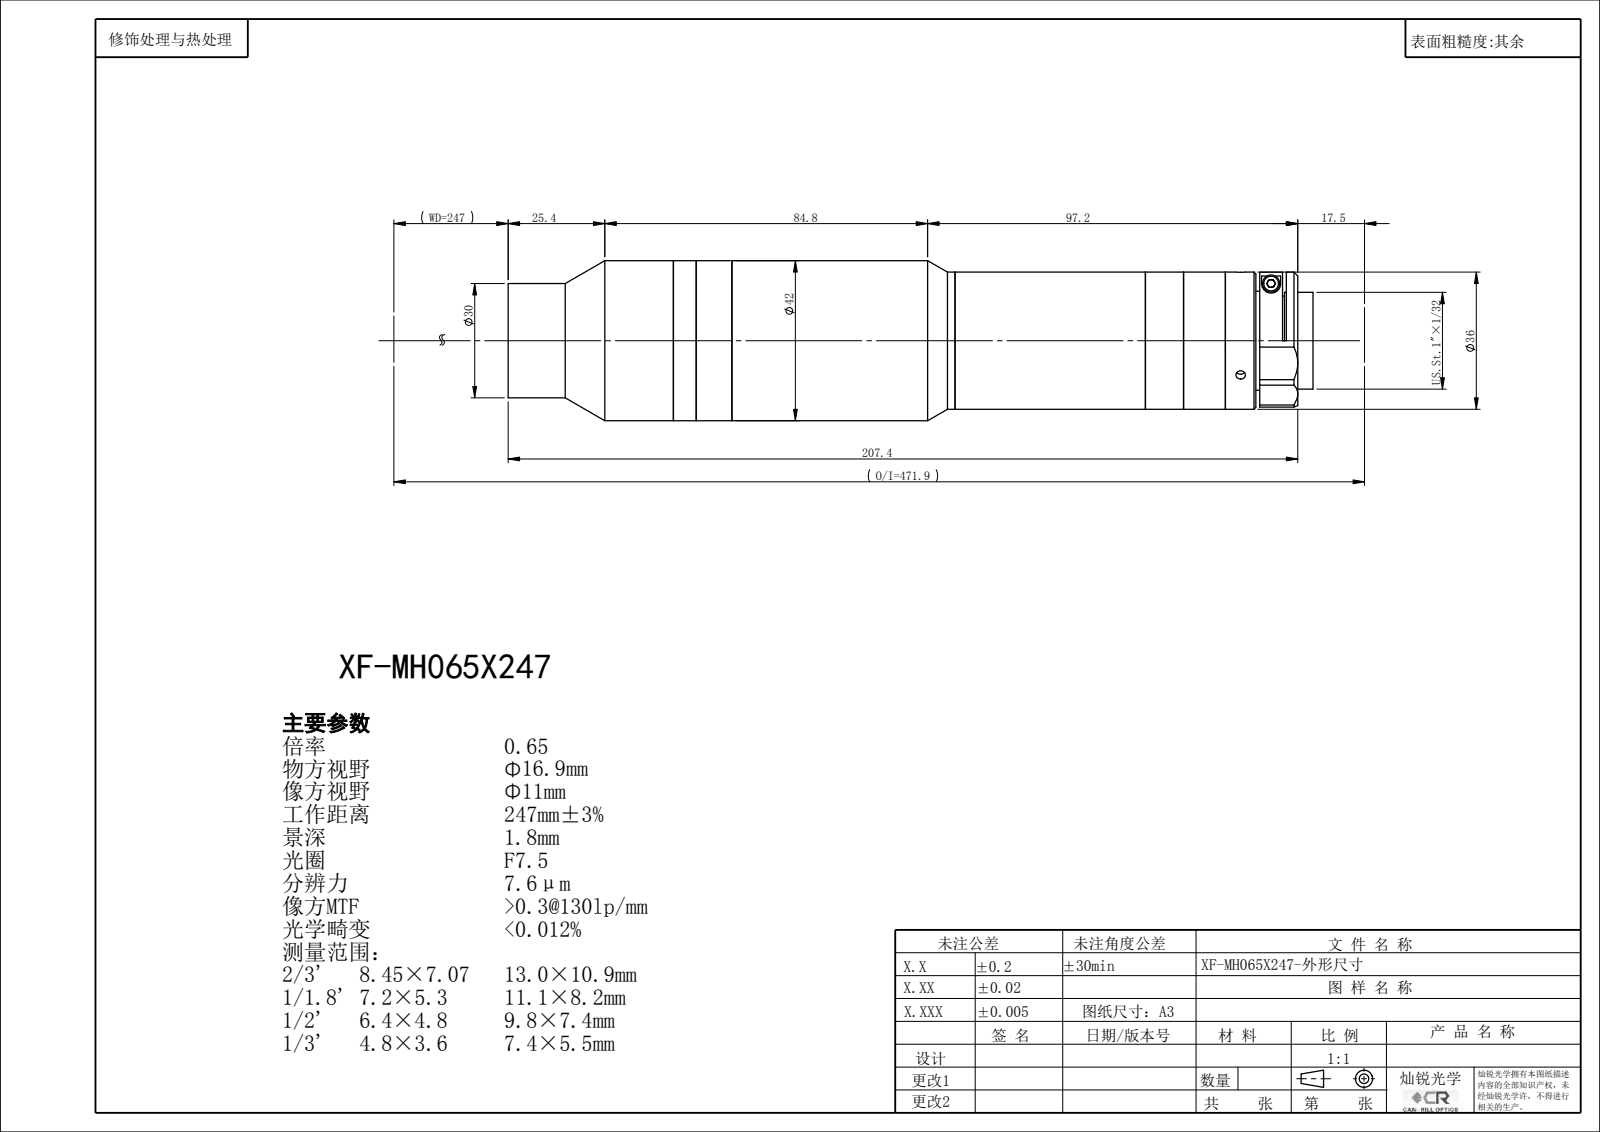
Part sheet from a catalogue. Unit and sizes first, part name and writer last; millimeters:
Units: millimetres
Overall size (bounding box): 211.73 × 42 × 42
Round holes (diameter × count): ⌀2.5 ×3, ⌀22.4 ×1, ⌀24 ×1, ⌀26.4 ×1
Round bosses / shafts (diameter × count): ⌀42 ×1, ⌀36 ×1, ⌀34 ×1, ⌀30 ×1, ⌀25.4 ×1
Main face-to-face distances: 1.5, 38.88, 40.38, 50, 88.88, 90.38, 71, 21, 17.88, 19.38
Bodies: 0 solids, 137 faces (67 planar, 46 cylindrical, 24 other)
Part name (STEP PRODUCT): XF-MH065X247
STEP written by: SolidWorks 2022 (CONFIG_CONTROL_DESIGN)
